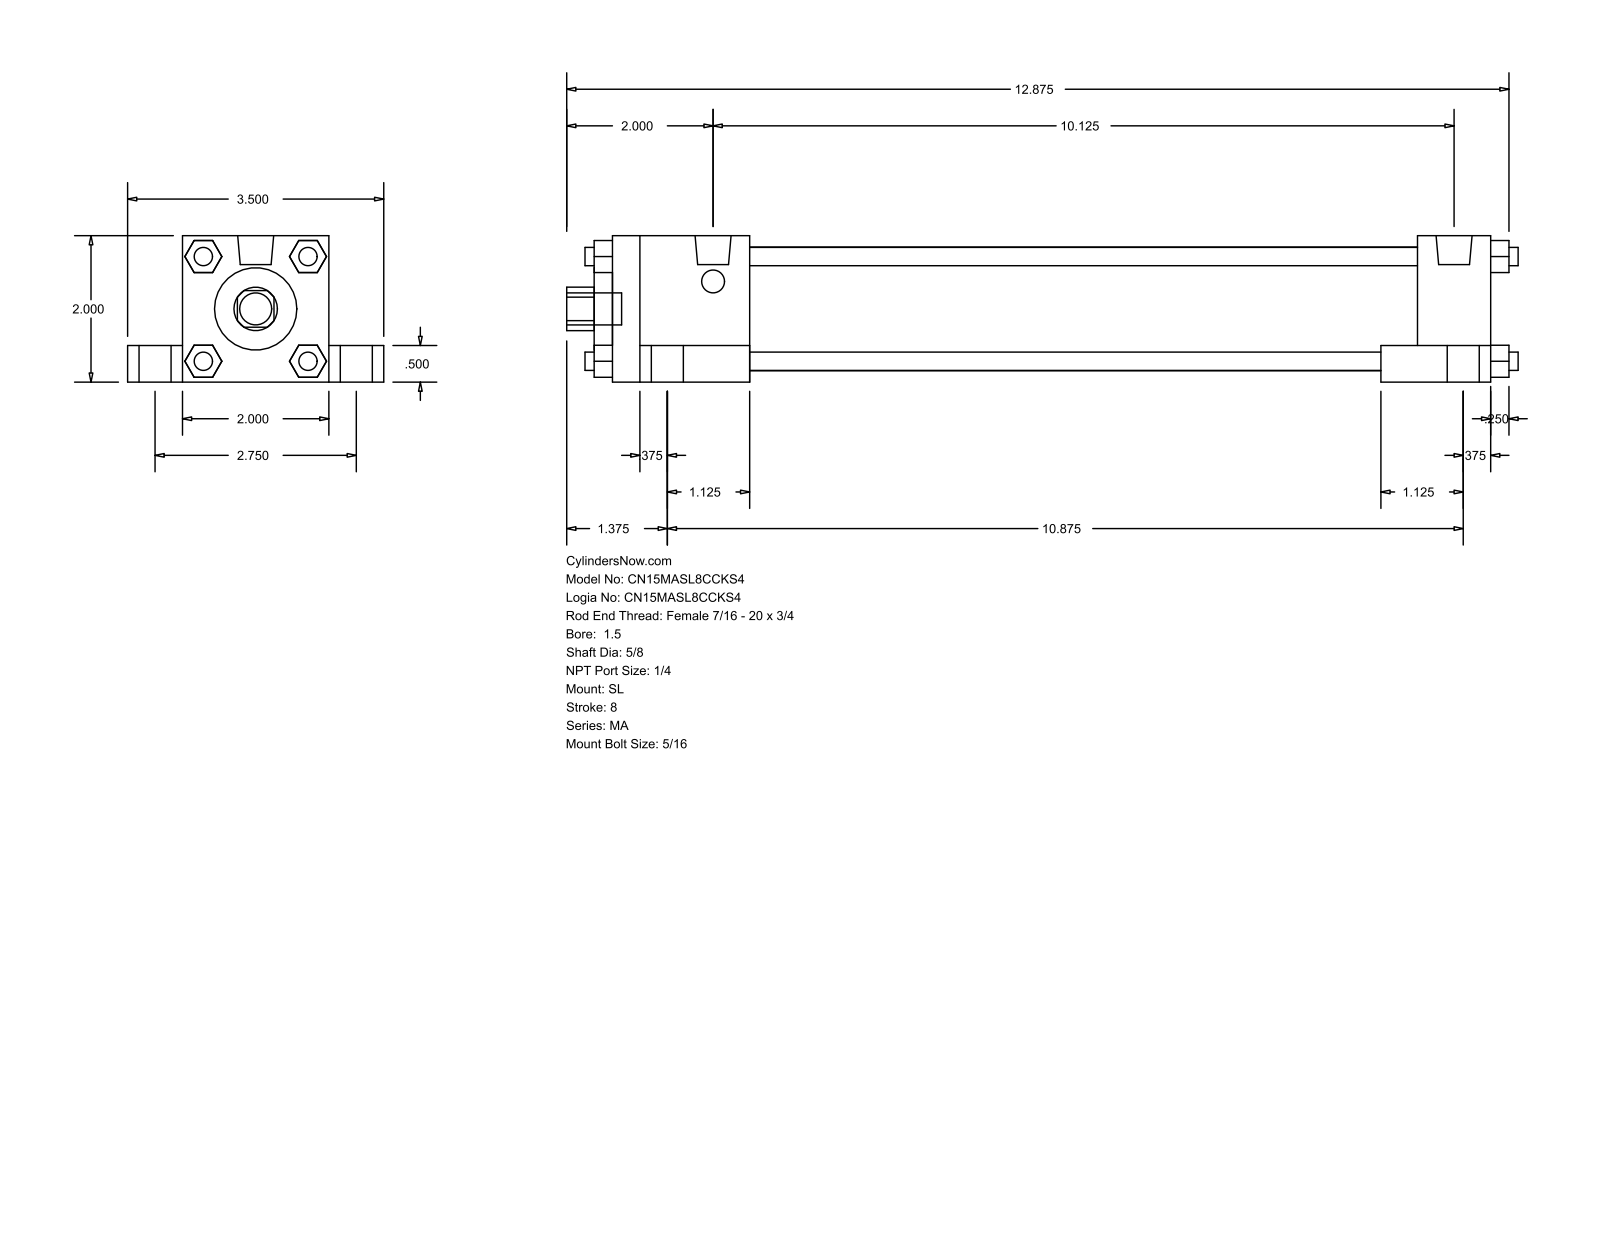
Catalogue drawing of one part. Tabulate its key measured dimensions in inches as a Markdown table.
| quantity | value |
| --- | --- |
| part name | MA_SL__0150_0.625 |
| STEP written by | GSSL Pune (CONFIG_CONTROL_DESIGN) |
| units | inches |
| bodies | 0 solids, 148 faces (112 planar, 36 cylindrical, 0 other) |
| overall size | 13 × 3.5 × 2 |
| round holes (diameter × count) | 0.625 × 1, 1.125 × 1, 1.69 × 1 |
| round bosses / shafts (diameter × count) | 0.437 × 5, 0.687 × 4, 0.313 × 4, 0.25 × 4, 0.492 × 2 |
| partial cylindrical surfaces (radius × count) | 0.297 × 1 |
| main face-to-face distances | 2, 0.75, 1.5, 0.5, 12, 2.75, 9.125, 0.375, 11, 1 |
